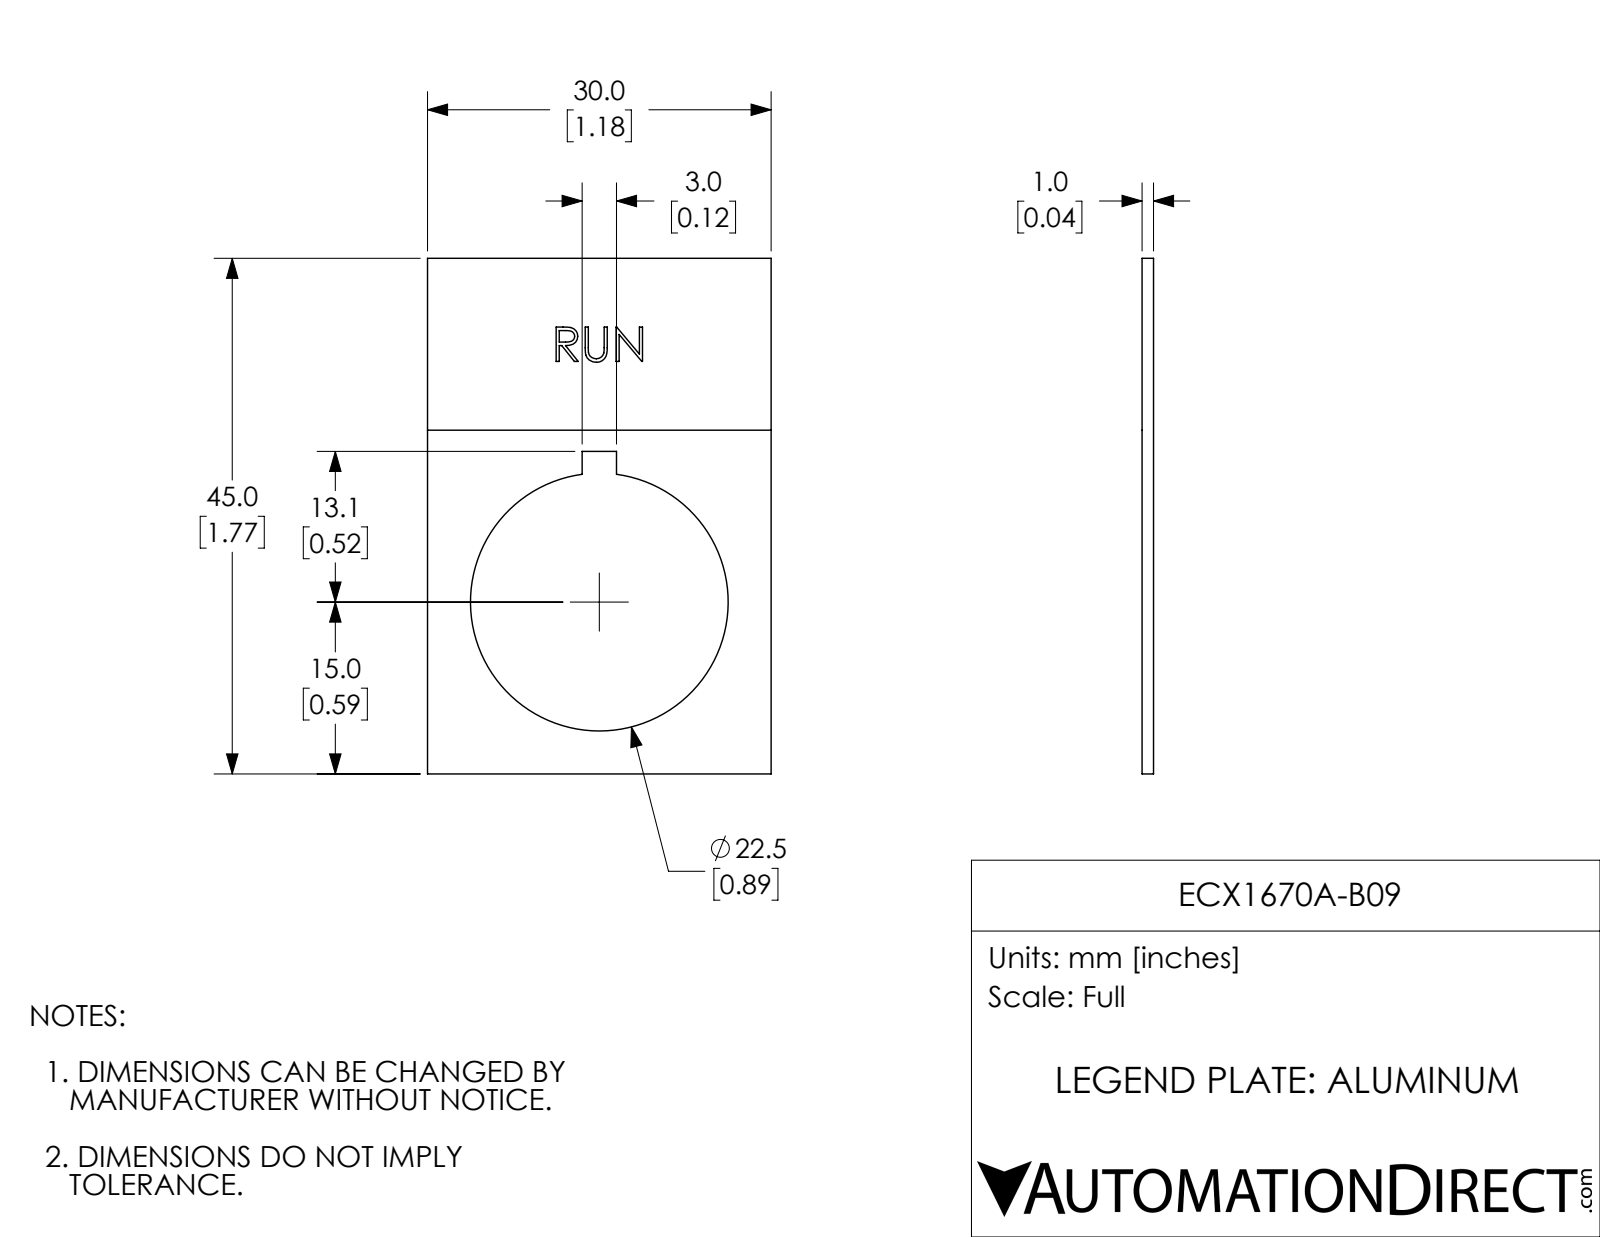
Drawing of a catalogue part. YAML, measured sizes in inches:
part_name: "ECX1670A-B09"
step_written_by: "SolidWorks 2017 (AUTOMOTIVE_DESIGN)"
units: inches
bodies: {solids: 1, faces: 56, planar: 41, cylindrical: 3, other: 12}
overall_size: [1.772, 1.181, 0.039]
volume: 0.058
surface_area: 3.285
round_holes:
  - {diameter: 0.886, count: 1}
face_to_face_distances: [0.039, 1.181, 1.772, 0.038, 0.531, 0.65, 1.108, 0.663, 0.118, 0.089]
